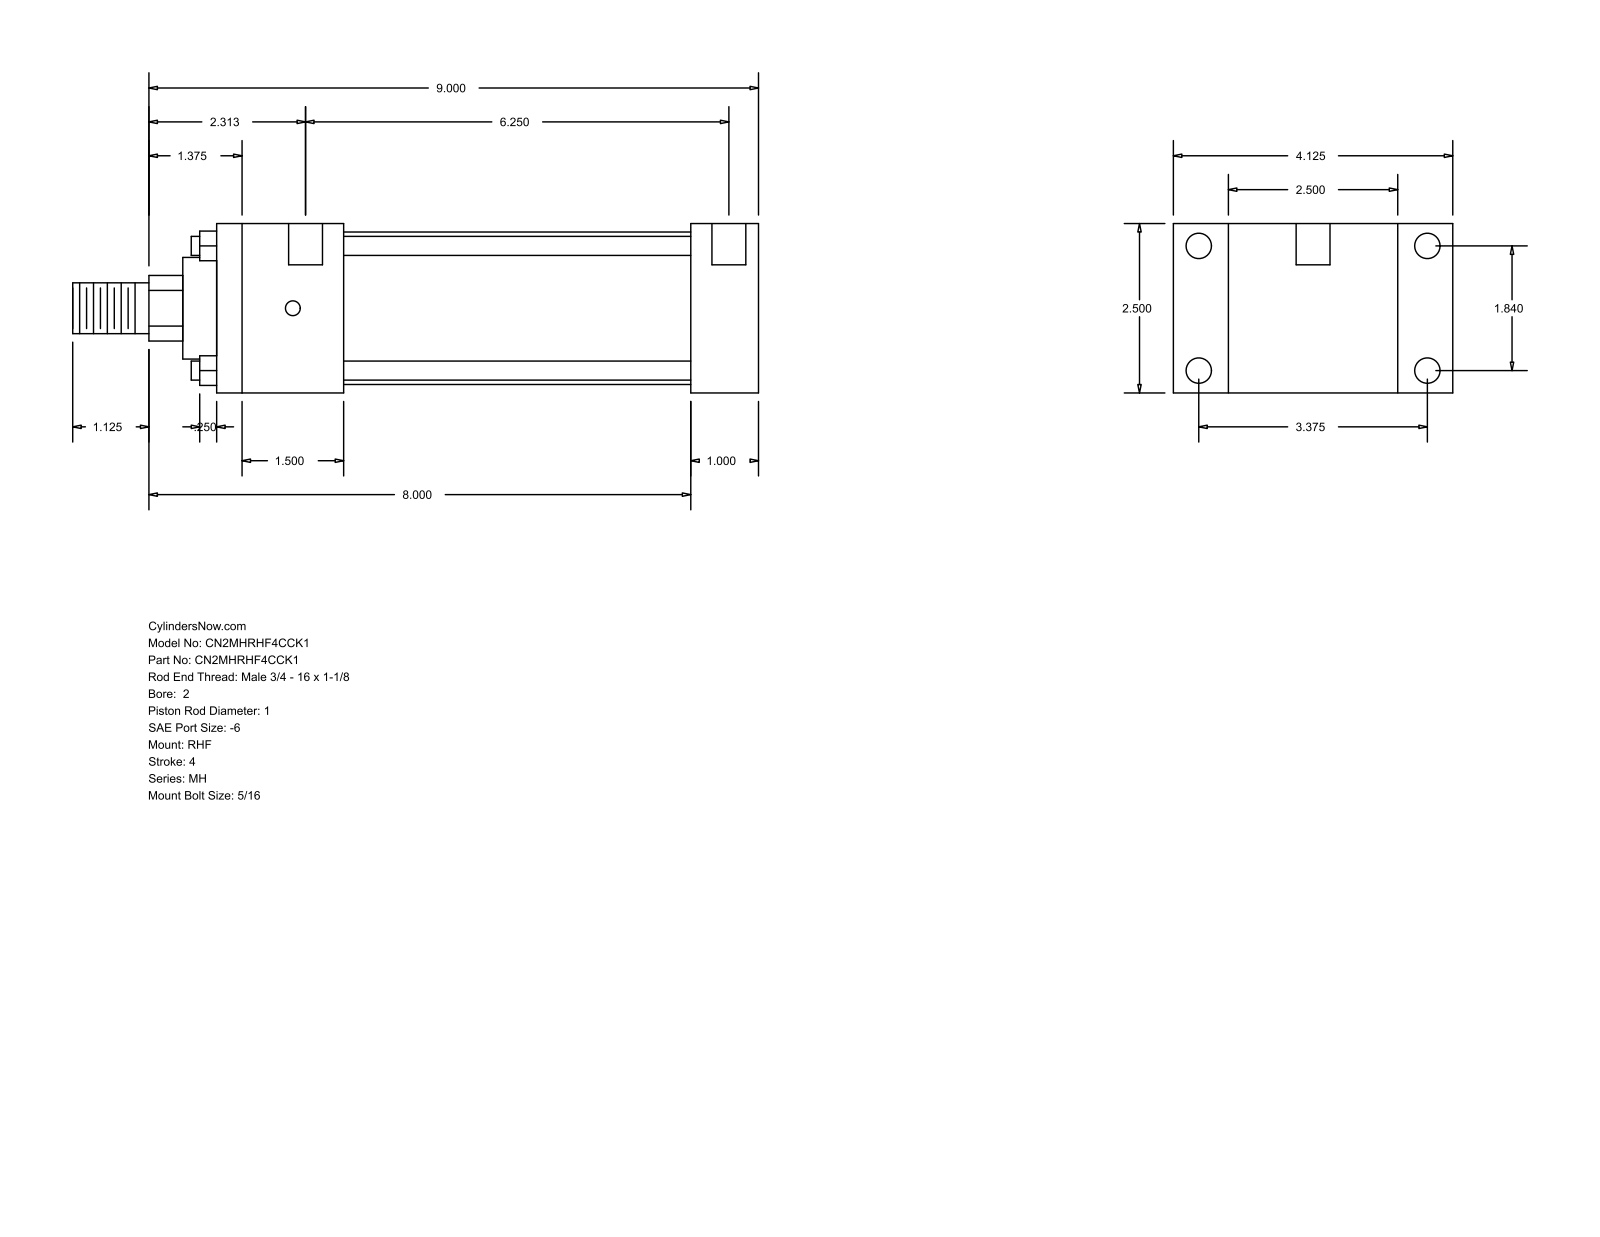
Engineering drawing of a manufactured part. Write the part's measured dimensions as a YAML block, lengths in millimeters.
part_name: "MH_RHF__0200_1"
step_written_by: "GSSL Pune (CONFIG_CONTROL_DESIGN)"
units: millimeters
bodies: {solids: 0, faces: 88, planar: 60, cylindrical: 28, other: 0}
overall_size: [257.18, 104.78, 63.5]
round_holes:
  - {diameter: 5.56, count: 4}
  - {diameter: 9.53, count: 4}
  - {diameter: 12.7, count: 2}
round_bosses_or_shafts:
  - {diameter: 7.14, count: 4}
  - {diameter: 57.15, count: 1}
  - {diameter: 38.1, count: 1}
  - {diameter: 25.4, count: 1}
  - {diameter: 19.05, count: 1}
partial_cylinders:
  - {radius: 12.29, count: 1}
face_to_face_distances: [63.5, 25.4, 20.64, 84.14, 203.2, 177.8, 104.78, 47.63, 130.17, 155.57]
hole_center_spacings: [46.74, 85.72, 97.63, 166.68, 3.17, 4.76, 158.75, 161.92]
